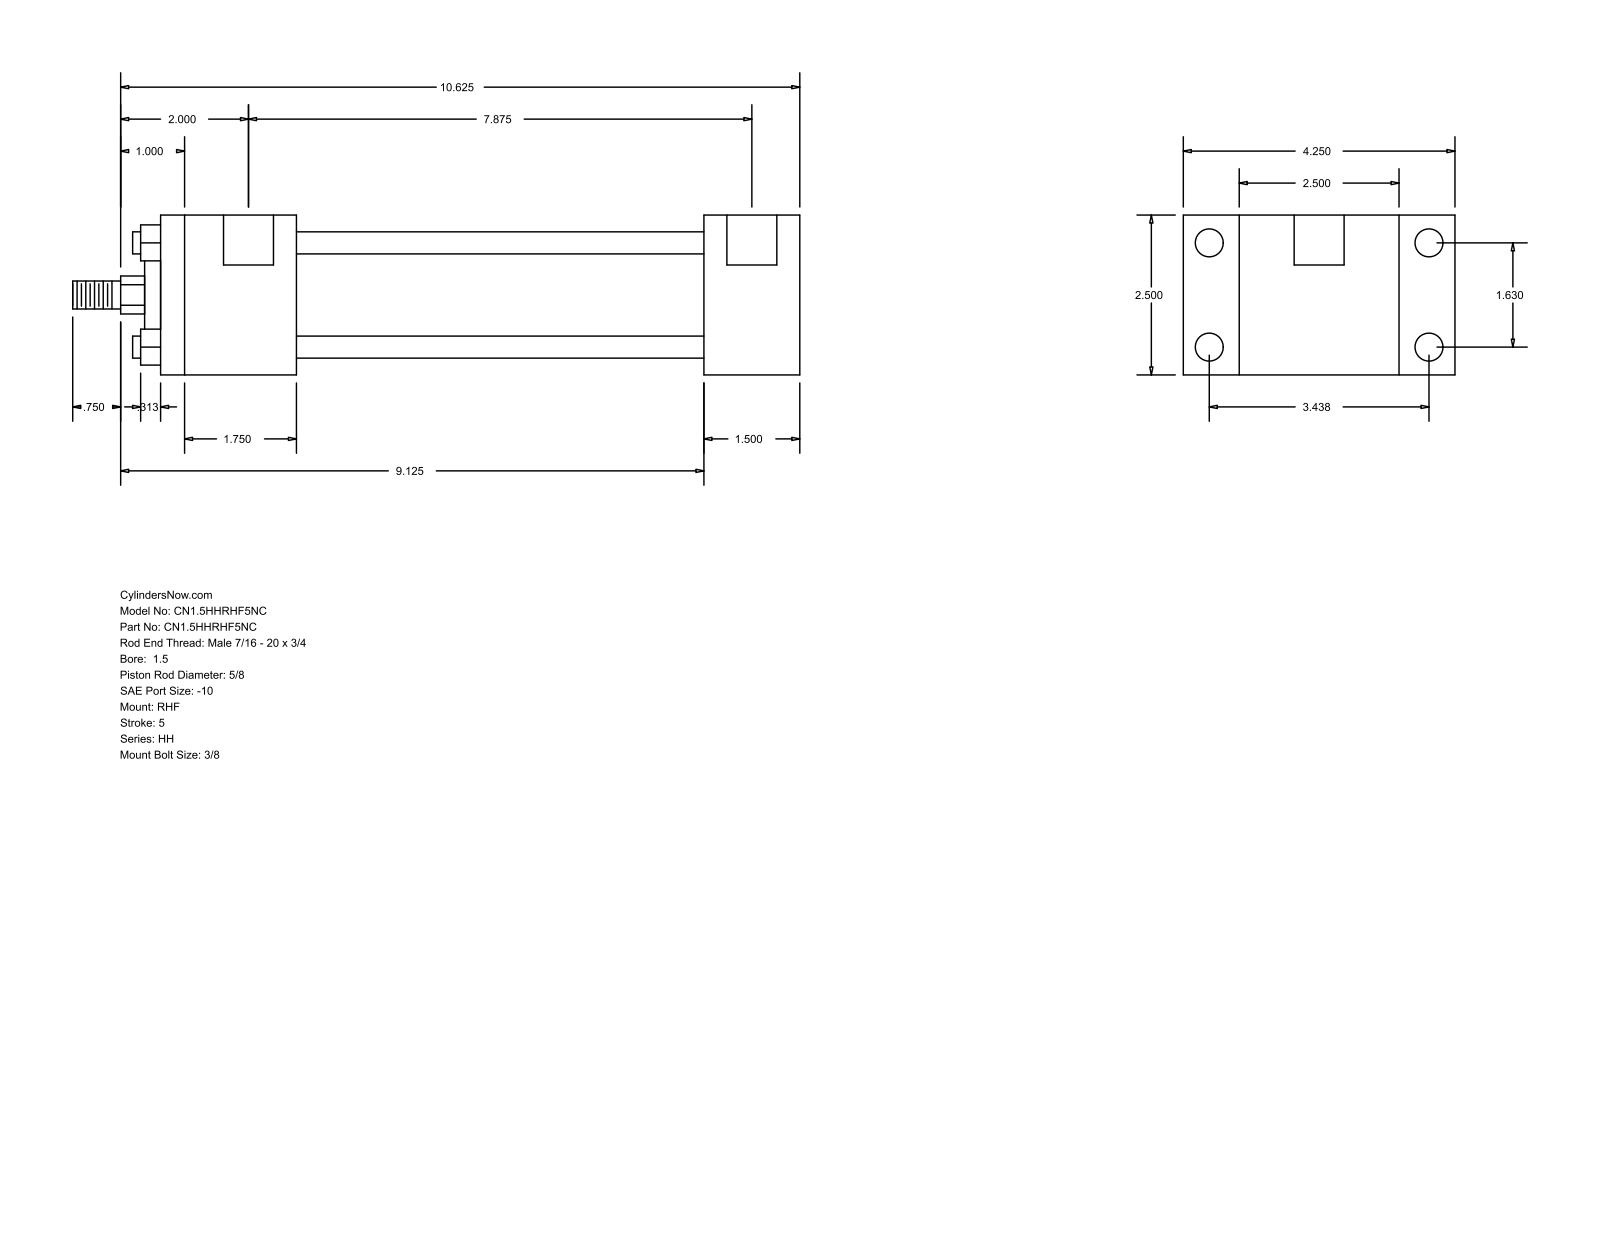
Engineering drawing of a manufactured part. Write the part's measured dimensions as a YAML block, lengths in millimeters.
part_name: "HH_RHF__0150_0.625"
step_written_by: "GSSL Pune (CONFIG_CONTROL_DESIGN)"
units: millimeters
bodies: {solids: 0, faces: 88, planar: 60, cylindrical: 28, other: 0}
overall_size: [288.93, 107.95, 63.5]
round_holes:
  - {diameter: 5.56, count: 4}
  - {diameter: 11.13, count: 4}
  - {diameter: 19.84, count: 2}
round_bosses_or_shafts:
  - {diameter: 8.76, count: 4}
  - {diameter: 44.45, count: 1}
  - {diameter: 28.57, count: 1}
  - {diameter: 15.88, count: 1}
  - {diameter: 11.11, count: 1}
partial_cylinders:
  - {radius: 7.54, count: 1}
face_to_face_distances: [63.5, 38.1, 22.23, 85.73, 215.9, 254, 107.96, 53.97, 161.93, 200.03]
hole_center_spacings: [1.59, 41.4, 87.32, 96.64, 201.61, 203.2, 200.02]
